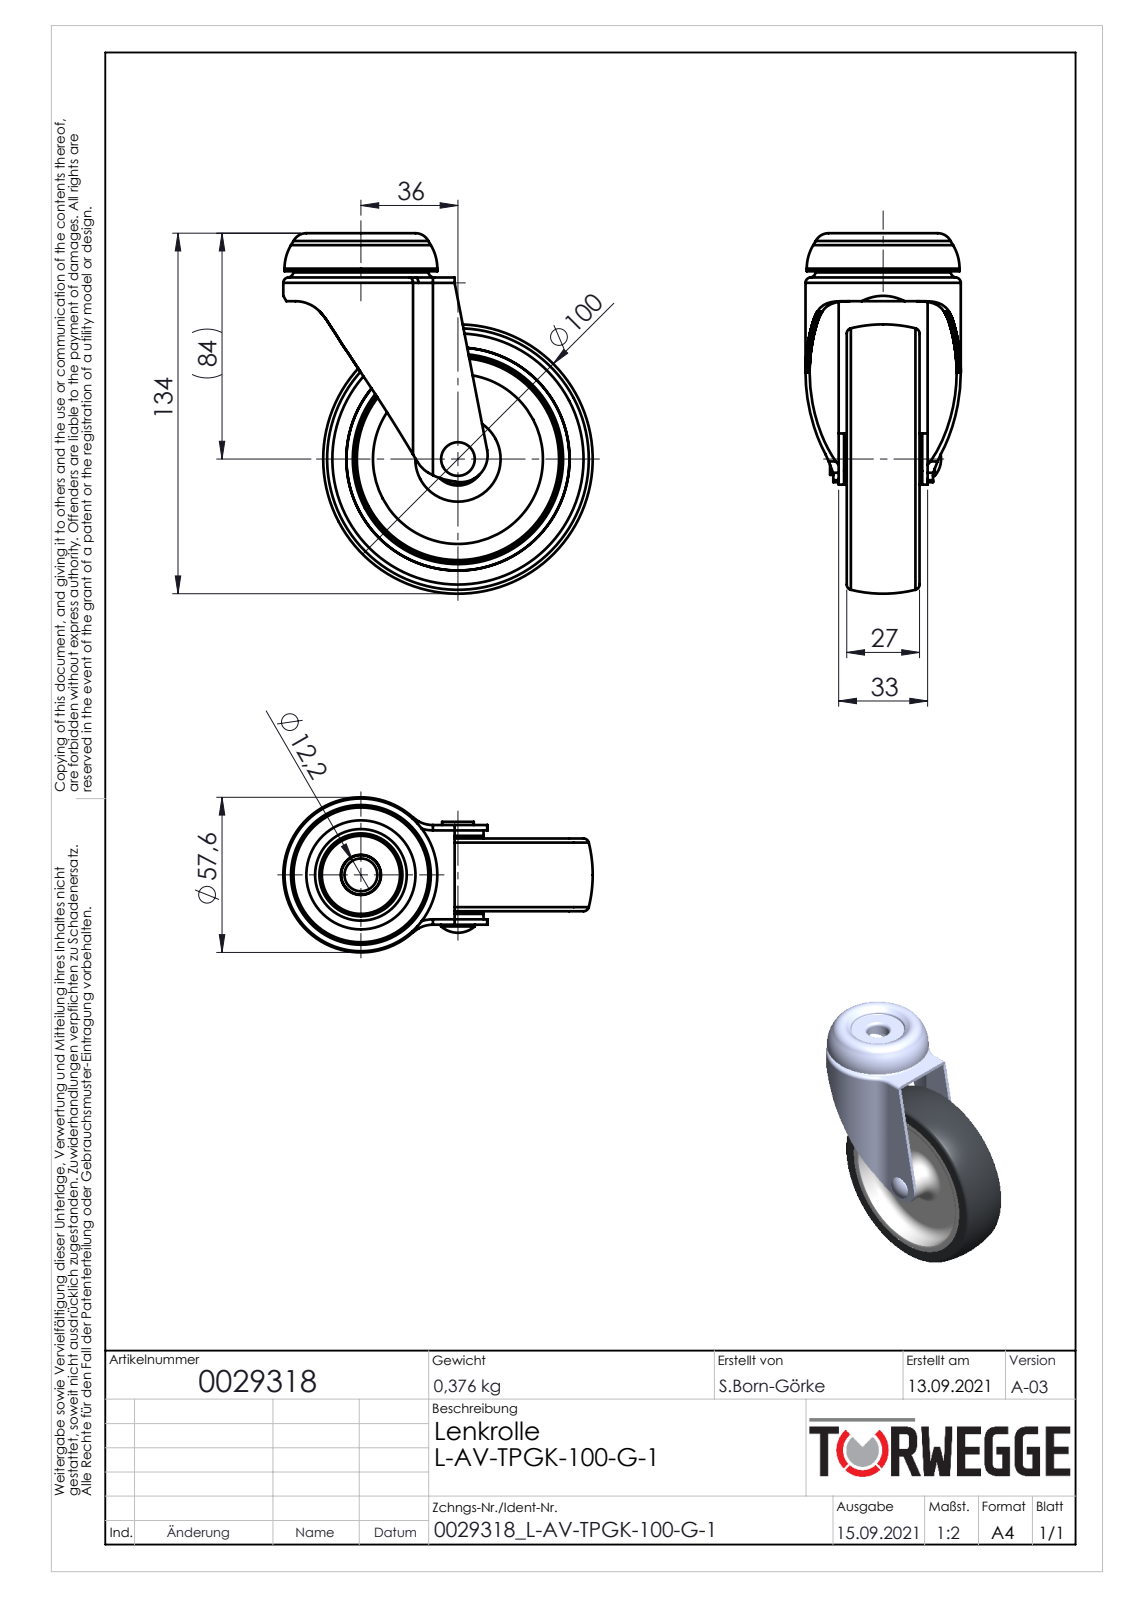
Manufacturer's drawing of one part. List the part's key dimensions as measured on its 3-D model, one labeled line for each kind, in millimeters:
Part name (STEP PRODUCT): 0029318
STEP written by: SolidWorks 2020 (AUTOMOTIVE_DESIGN)
Units: millimetres
Bodies: 4 solids, 519 faces (263 planar, 59 cylindrical, 197 other)
Overall size (bounding box): 133.85 × 114.8 × 57.6
Volume: 160 828 mm³ · Surface area: 84 628 mm²
Round holes (diameter × count): ⌀5.6 ×1, ⌀8.2 ×1, ⌀12.25 ×1, ⌀12.3 ×1, ⌀12.6 ×1, ⌀52.5 ×1, ⌀82.8 ×1, ⌀92 ×1
Round bosses / shafts (diameter × count): ⌀56.7 ×1, ⌀19 ×1, ⌀12.5 ×1, ⌀11.76 ×1, ⌀8 ×1
Partial cylindrical surfaces — rounded edges, fillets, slot ends (radius × count): R2 ×2, R11 ×2, R10 ×1, R12 ×1, R12.5 ×1, R22 ×1, R27.27 ×1, R28.8 ×1
Main face-to-face distances: 11.25, 15.75, 3, 14.25, 18.75, 30, 2, 4.5, 4.25, 14.5
